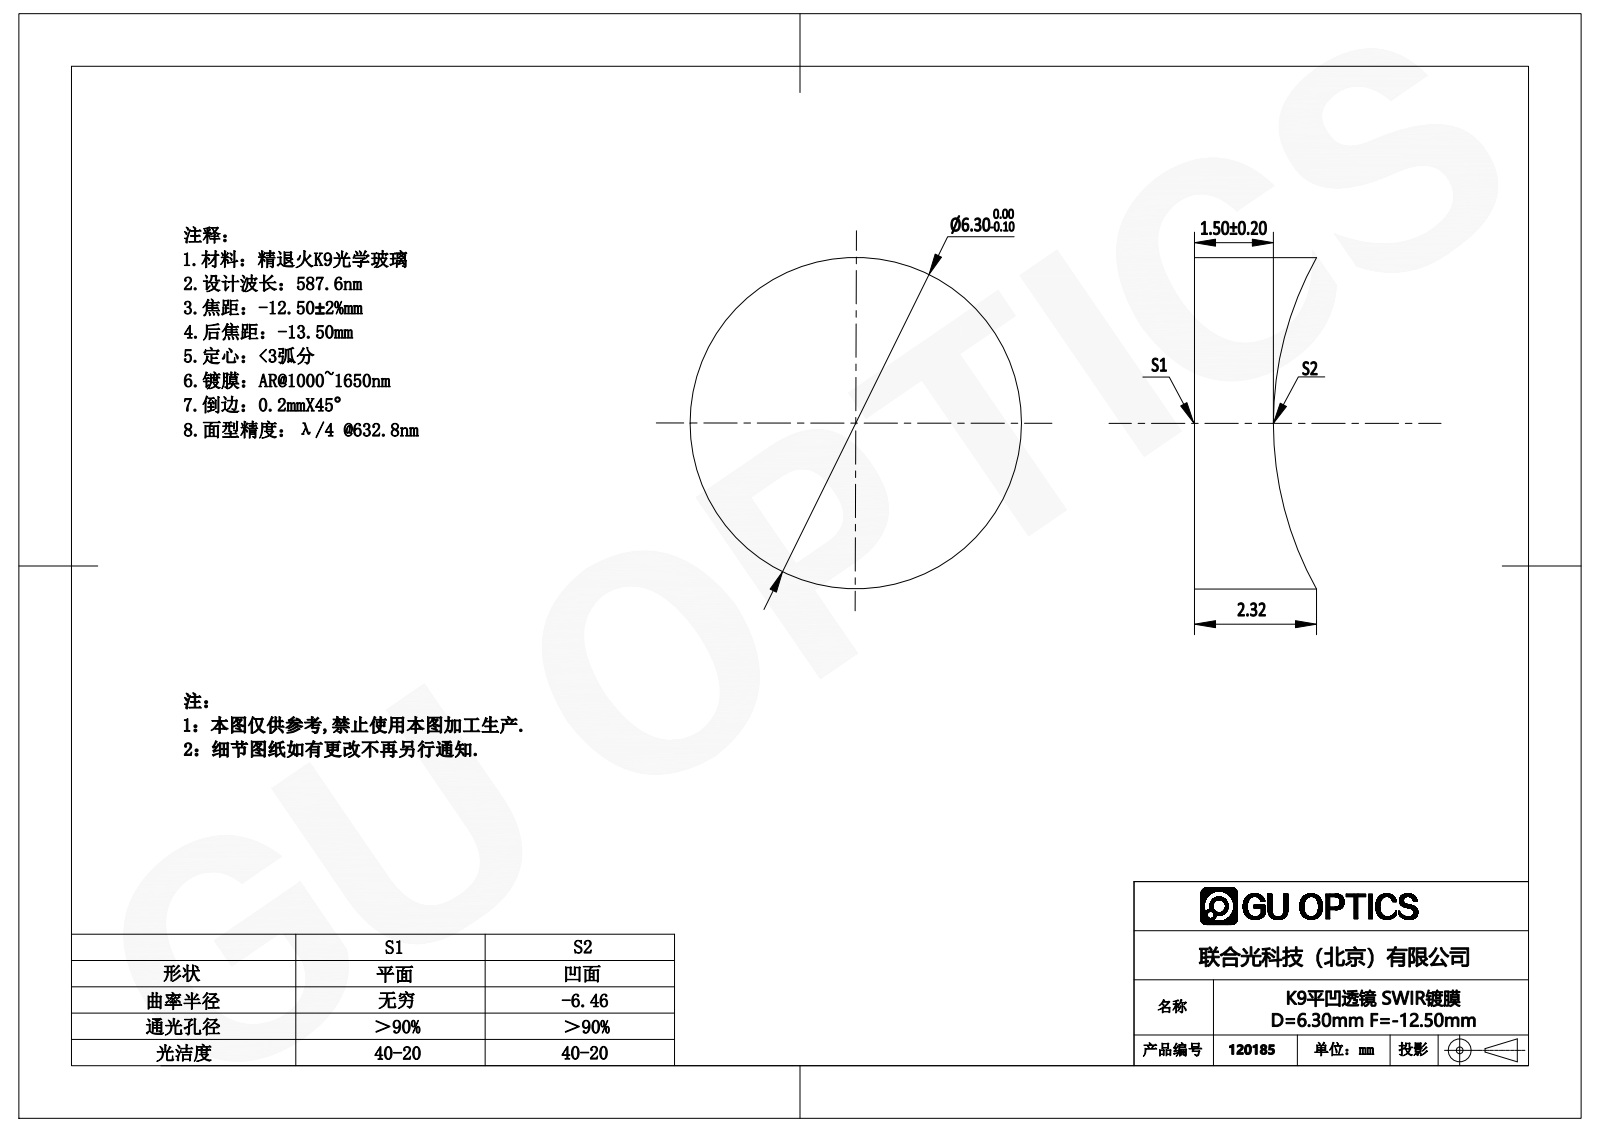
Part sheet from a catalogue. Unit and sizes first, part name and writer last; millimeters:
Units: millimetres
Overall size (bounding box): 6.3 × 6.3 × 2.32
Round bosses / shafts (diameter × count): ⌀6.3 ×1
Volume: 59 mm³ · Surface area: 110 mm²
Bodies: 1 solid, 5 faces (1 planar, 2 cylindrical, 2 other)
Part name (STEP PRODUCT): 120125
STEP written by: SolidWorks 2016 (AUTOMOTIVE_DESIGN)
